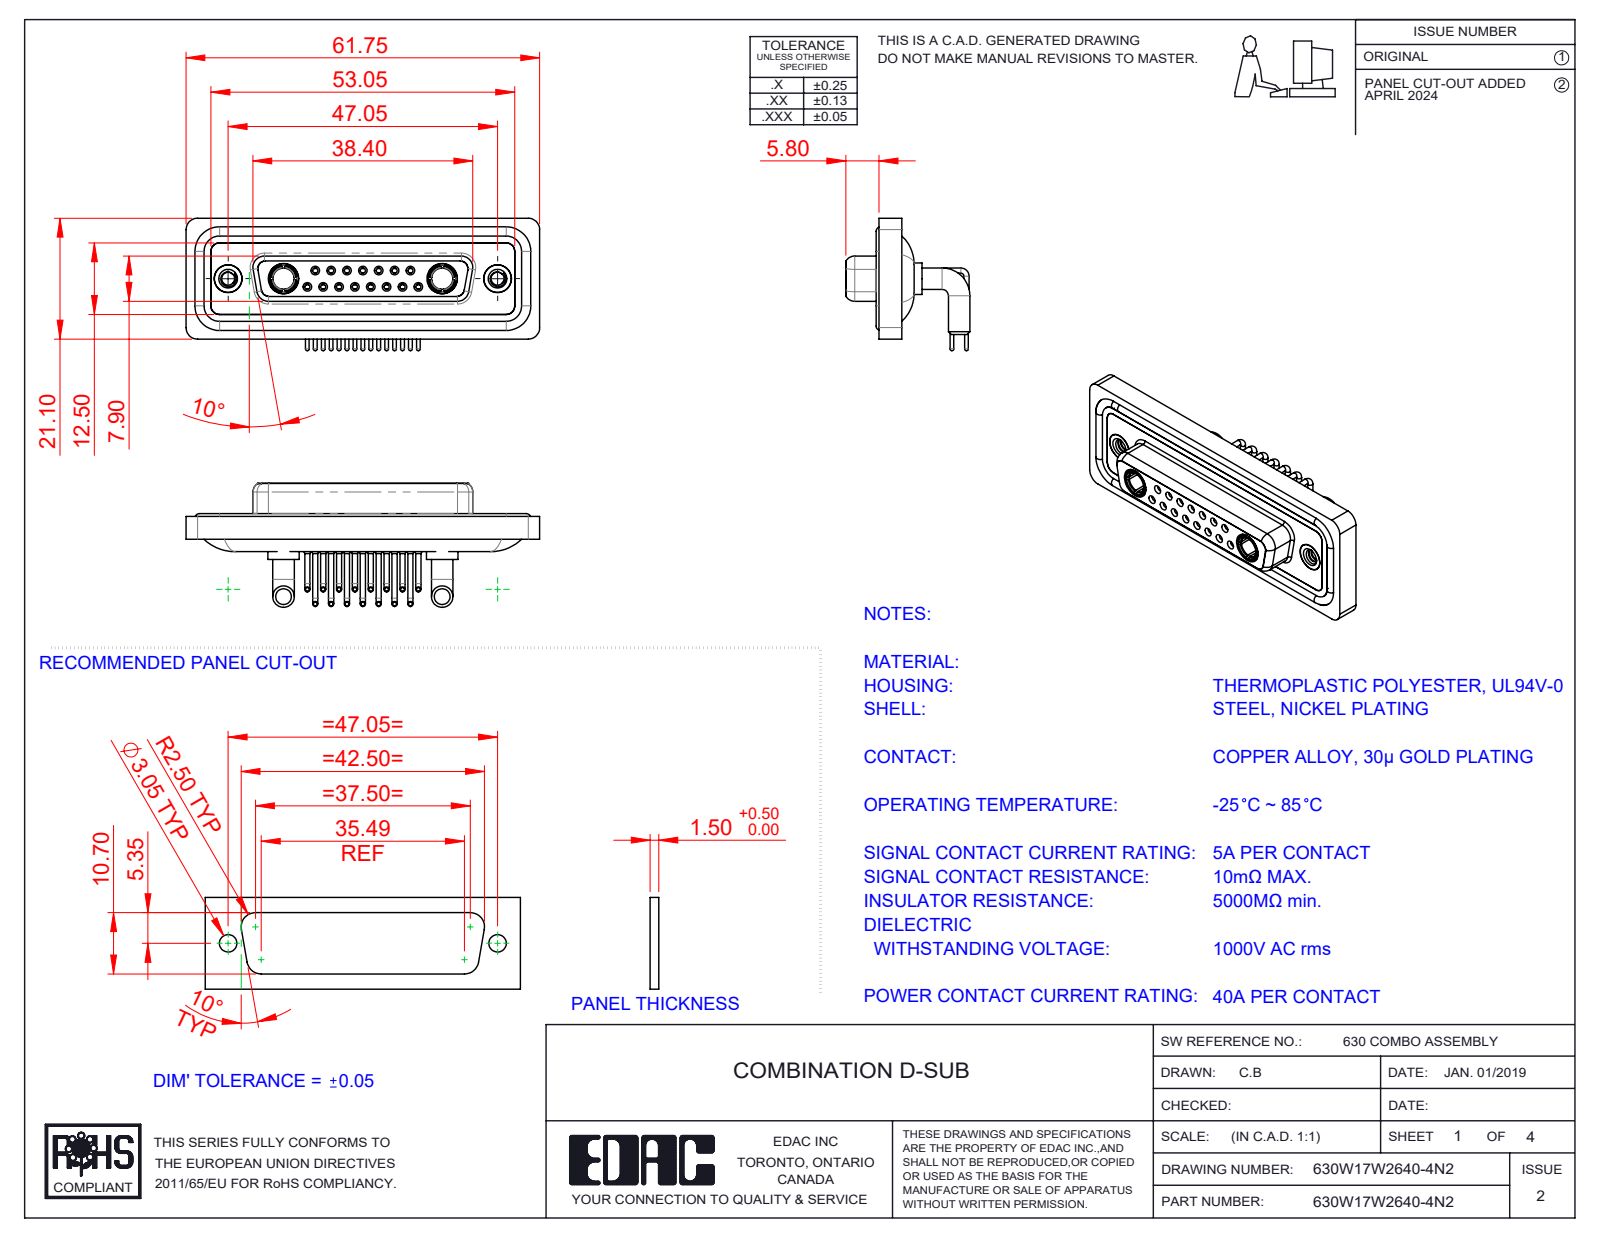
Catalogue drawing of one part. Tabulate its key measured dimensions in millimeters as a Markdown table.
| quantity | value |
| --- | --- |
| part name | 630W17W2640-4N2; 630Combo Housing_17W2; 630Combo Waterproof Housing_25 Contacts; 630Combo Shell Rear_25 Contacts (+5 more) |
| STEP written by | SolidWorks 2023 (CONFIG_CONTROL_DESIGN) |
| units | millimeters |
| bodies | 26 solids, 1337 faces (388 planar, 583 cylindrical, 366 other) |
| overall size | 61.75 × 23.12 × 21.68 |
| volume | 8 632 mm³ |
| surface area | 14 618 mm² |
| round holes (diameter × count) | 0.9 × 15, 1.1 × 15, 1.5 × 15, 2 × 15, 1.6 × 8, 1.7 × 7, 4.85 × 4, 2.26 × 2, 3.7 × 2, 4 × 2, 4.05 × 2, 5 × 2 |
| round bosses / shafts (diameter × count) | 0.9 × 15, 0.65 × 15, 1.6 × 11, 3.75 × 4, 5.5 × 2, 5.2 × 2, 4.96 × 2, 4.95 × 2 |
| partial cylindrical surfaces (radius × count) | 1.5 × 18, 2 × 18, 1.35 × 8, 1.6 × 8, 0.25 × 4, 0.5 × 4, 0.6 × 4, 0.65 × 4 |
| main face-to-face distances | 0.4, 1.8, 4.1, 1.1, 1.6, 3.1, 2.5, 1.5, 3.7, 1.4 |
| hole center spacings | 3.16, 2.77, 5.54, 8.31, 5.04, 7.49, 11.08, 5.03 |
